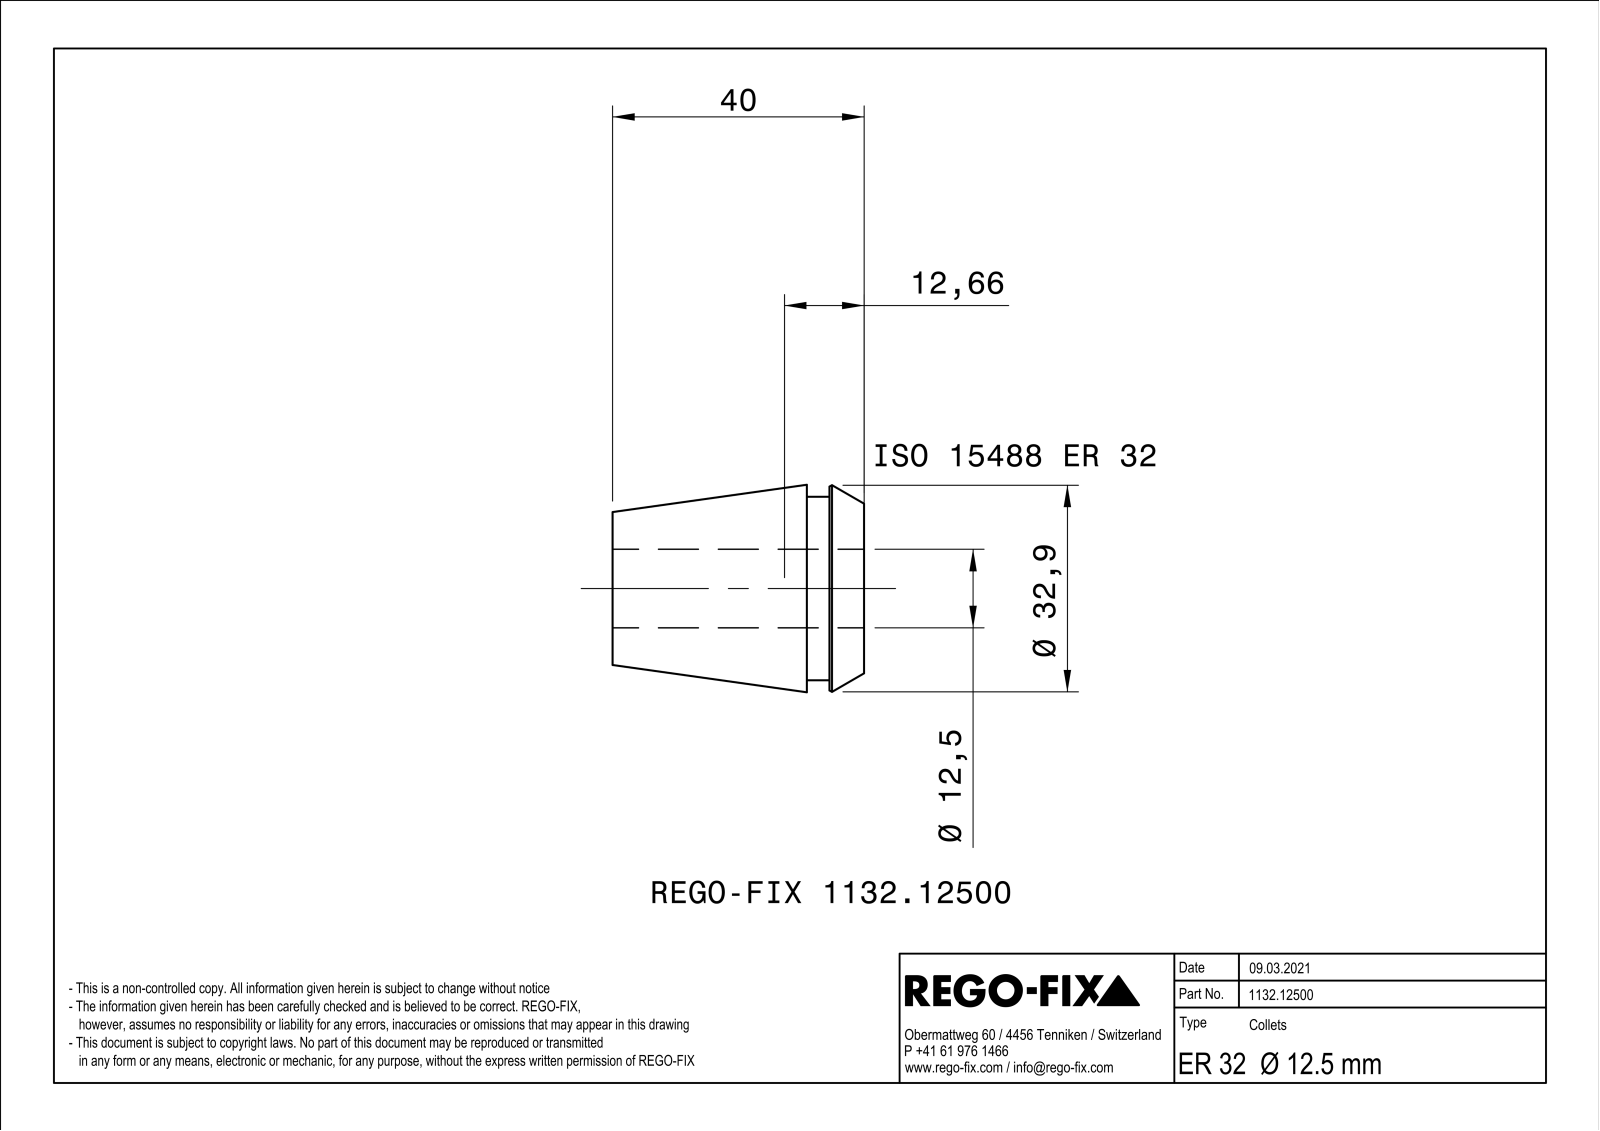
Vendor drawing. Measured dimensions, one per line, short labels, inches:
name: NOCUT
written by: SIEMENS PLM Software Solid Edge ST10 (AUTOMOTIVE_DESIGN)
unit: in
bodies: 1 solid, 209 faces (88 planar, 41 cylindrical, 80 other)
size: 1.575 × 1.298 × 1.298
volume: 1.028 in³; area: 22.6 in²
holes: 1× ⌀0.492
bosses: 1× ⌀1.15
rounds: 20× R0.016
face distances: 0.039, 1.575, 0.358, 1.217, 0.217, 0.142, 1.358, 0.236, 0.02, 0.122
